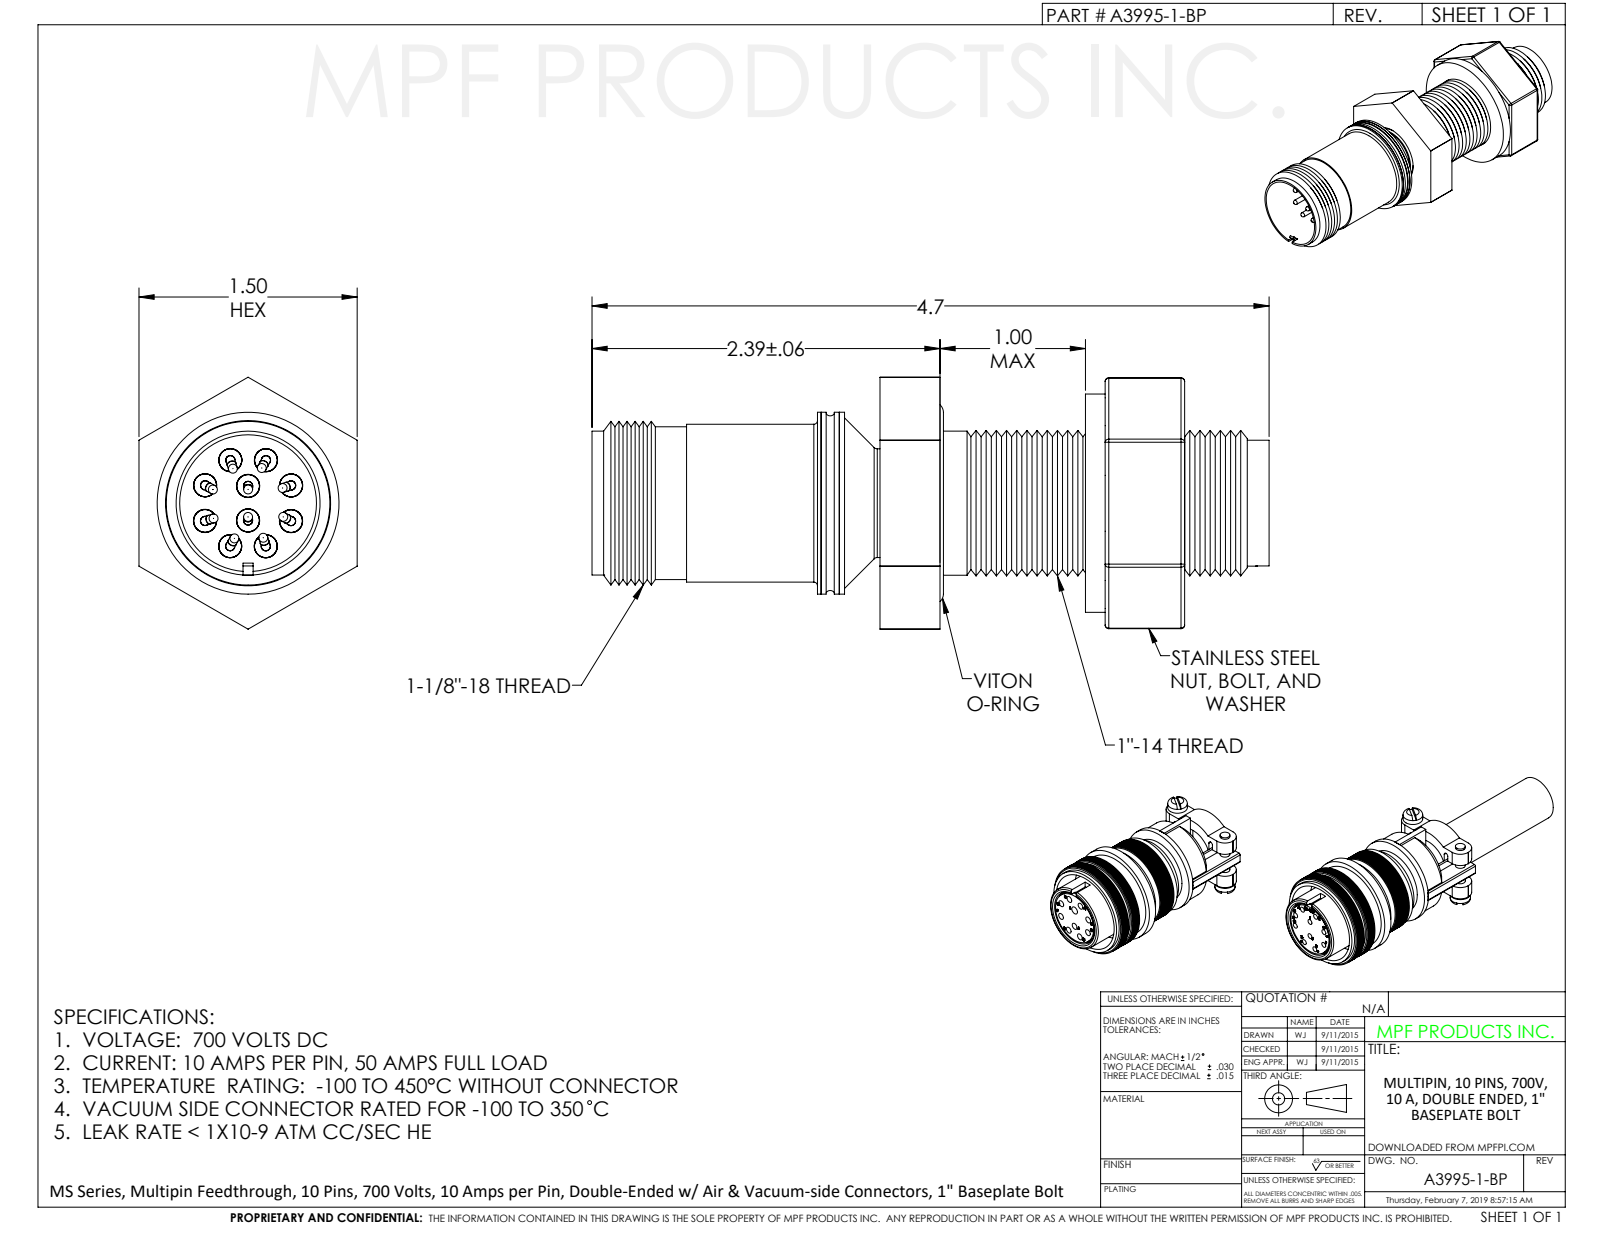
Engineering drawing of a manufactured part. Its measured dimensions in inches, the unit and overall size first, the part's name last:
Units: inches
Overall size (bounding box): 4.655 × 1.731 × 1.538
Round holes (diameter × count): ⌀0.07 ×42, ⌀0.063 ×10, ⌀0.064 ×10, ⌀0.141 ×10, ⌀0.157 ×10, ⌀0.159 ×10, ⌀0.63 ×1, ⌀0.687 ×1, ⌀0.752 ×1, ⌀0.815 ×1, ⌀0.94 ×1, ⌀0.96 ×1
Round bosses / shafts (diameter × count): ⌀0.062 ×50, ⌀0.187 ×10, ⌀0.157 ×10, ⌀1.5 ×1, ⌀1.369 ×1, ⌀1.25 ×1, ⌀1.11 ×1, ⌀1.085 ×1
Partial cylindrical surfaces — rounded edges, fillets, slot ends (radius × count): R0.025 ×18, R0.866 ×1
Main face-to-face distances: 1.5, 1.548, 0.546, 2.094, 0.125, 0.405, 0.682, 0.136, 1.412, 0.43
Hole centre spacings: 0.467, 0.193, 0.357, 0.434, 0.251, 0.106, 0.252, 0.37
Volume: 2.924 in³ · Surface area: 73.43 in²
Bodies: 41 solids, 1001 faces (108 planar, 407 cylindrical, 486 other)
Part name (STEP PRODUCT): A3995-1-BP
STEP written by: SolidWorks 2012 (CONFIG_CONTROL_DESIGN)
